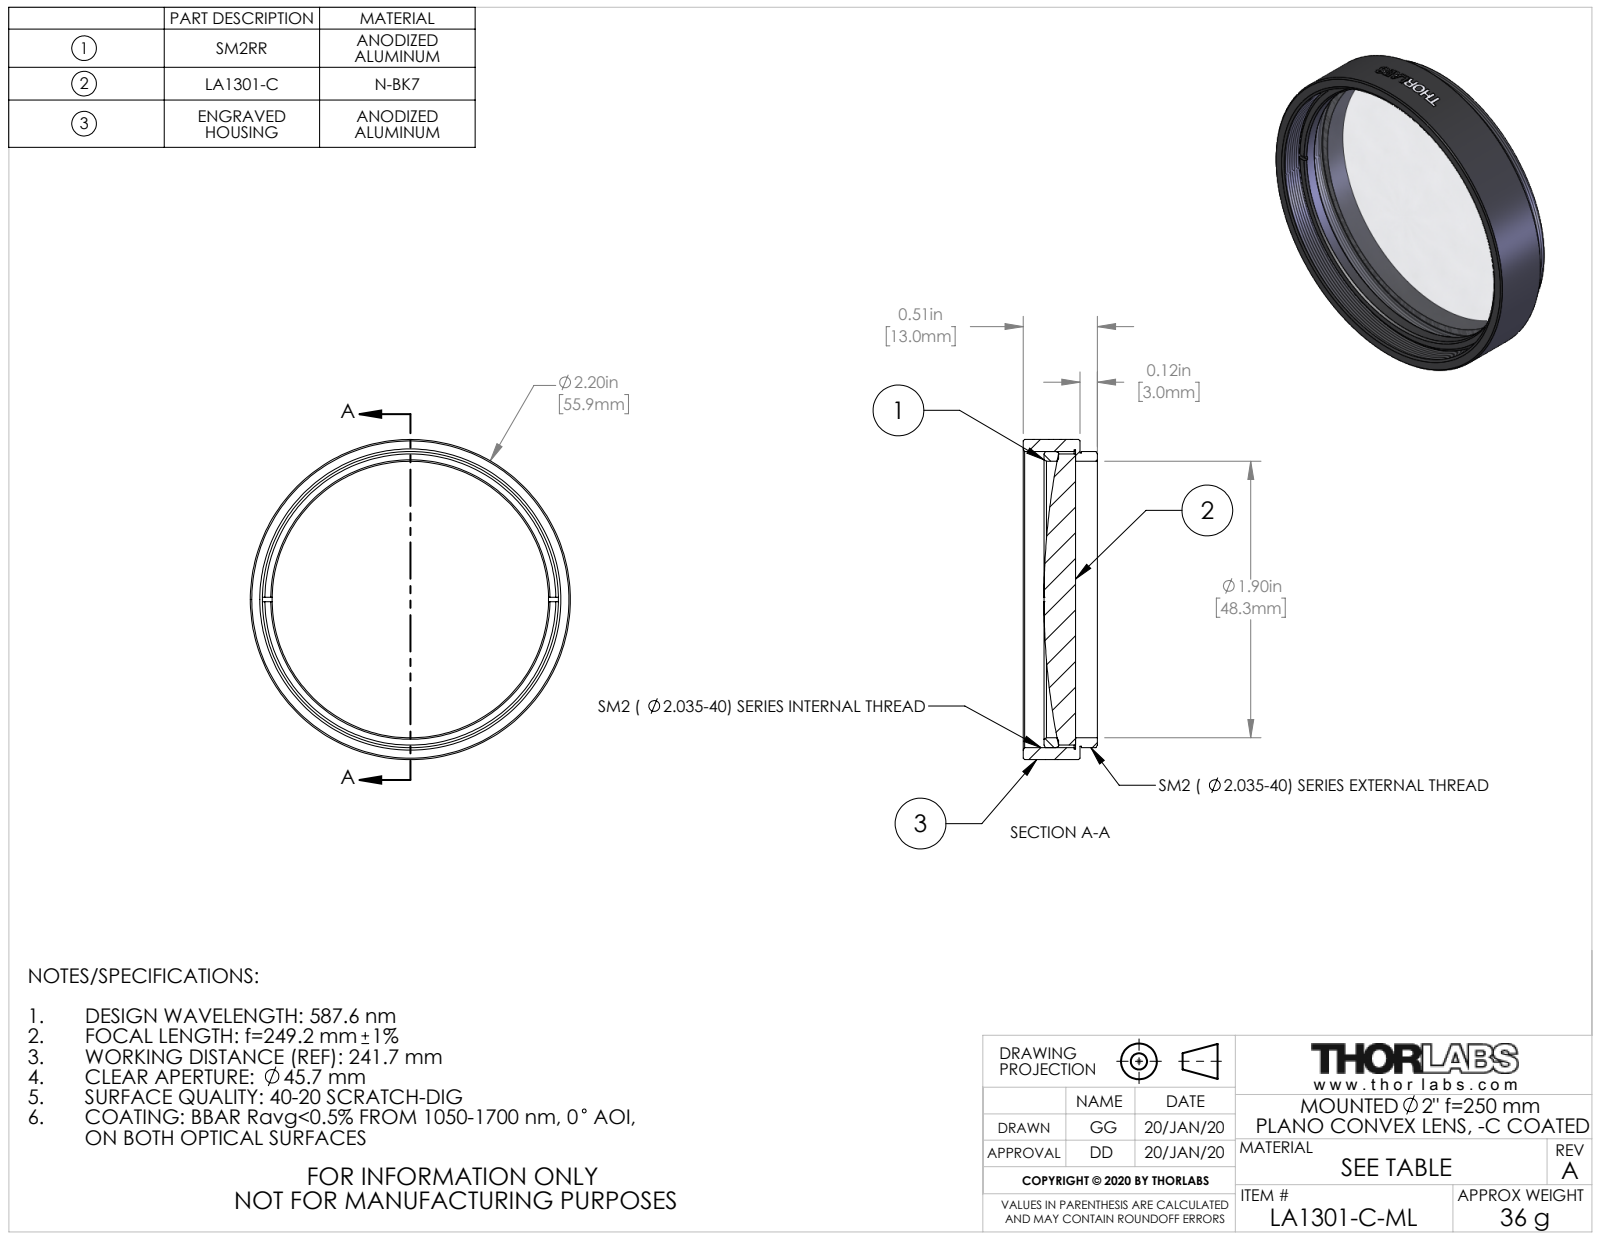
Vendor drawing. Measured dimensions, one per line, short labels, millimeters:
name: TTN203754-E0W
written by: SolidWorks 2018 (CONFIG_CONTROL_DESIGN)
unit: mm
bodies: 3 solids, 152 faces (16 planar, 112 cylindrical, 24 other)
size: 55.88 × 55.88 × 12.95
volume: 13 761 mm³; area: 11 356 mm²
holes: 1× ⌀48.26, 1× ⌀52.2
bosses: 1× ⌀55.88, 1× ⌀51.69, 1× ⌀51.18, 1× ⌀50.8
face distances: 0.76, 9.91, 9.15, 3.05, 3.81, 12.96, 6.8, 3.75, 2.99, 6.16
